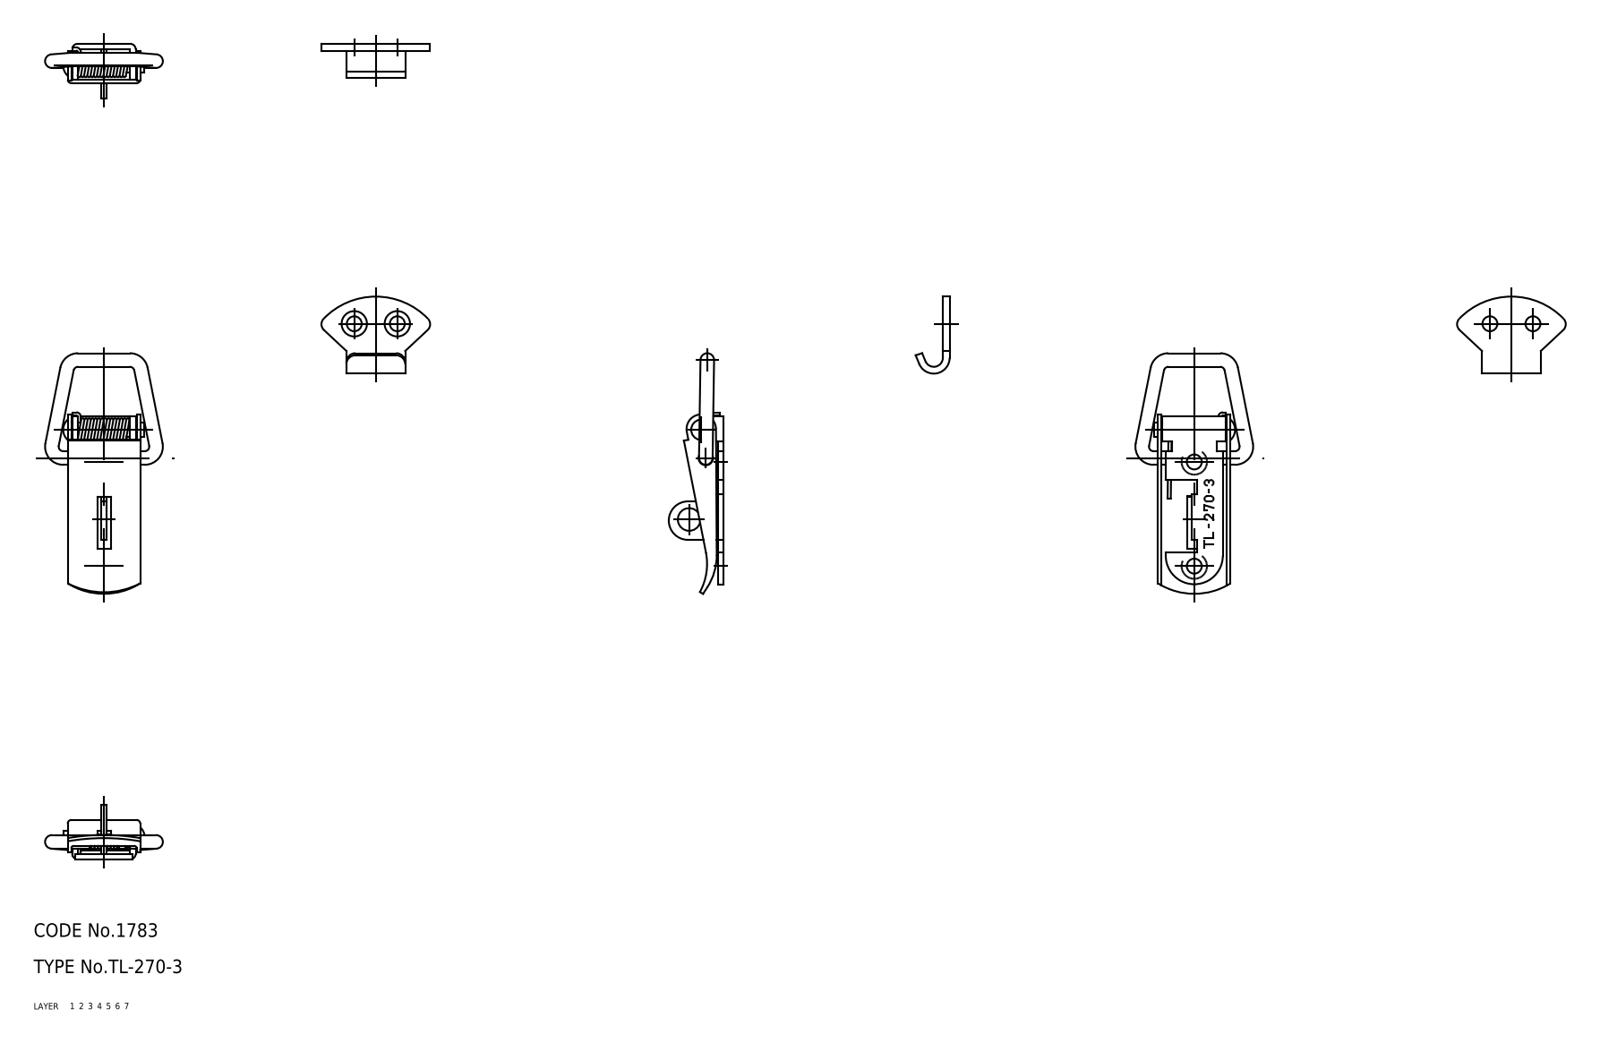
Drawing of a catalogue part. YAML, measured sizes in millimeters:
part_name: "67130226; 67130239; 67130252; 67130265 (+2 more)"
step_written_by: "CADfix (AUTOMOTIVE_DESIGN)"
units: millimeters
bodies: {solids: 6, faces: 305, planar: 0, cylindrical: 0, other: 305}
overall_size: [65.61, 25.99, 12]
volume: 2284
surface_area: 4876
